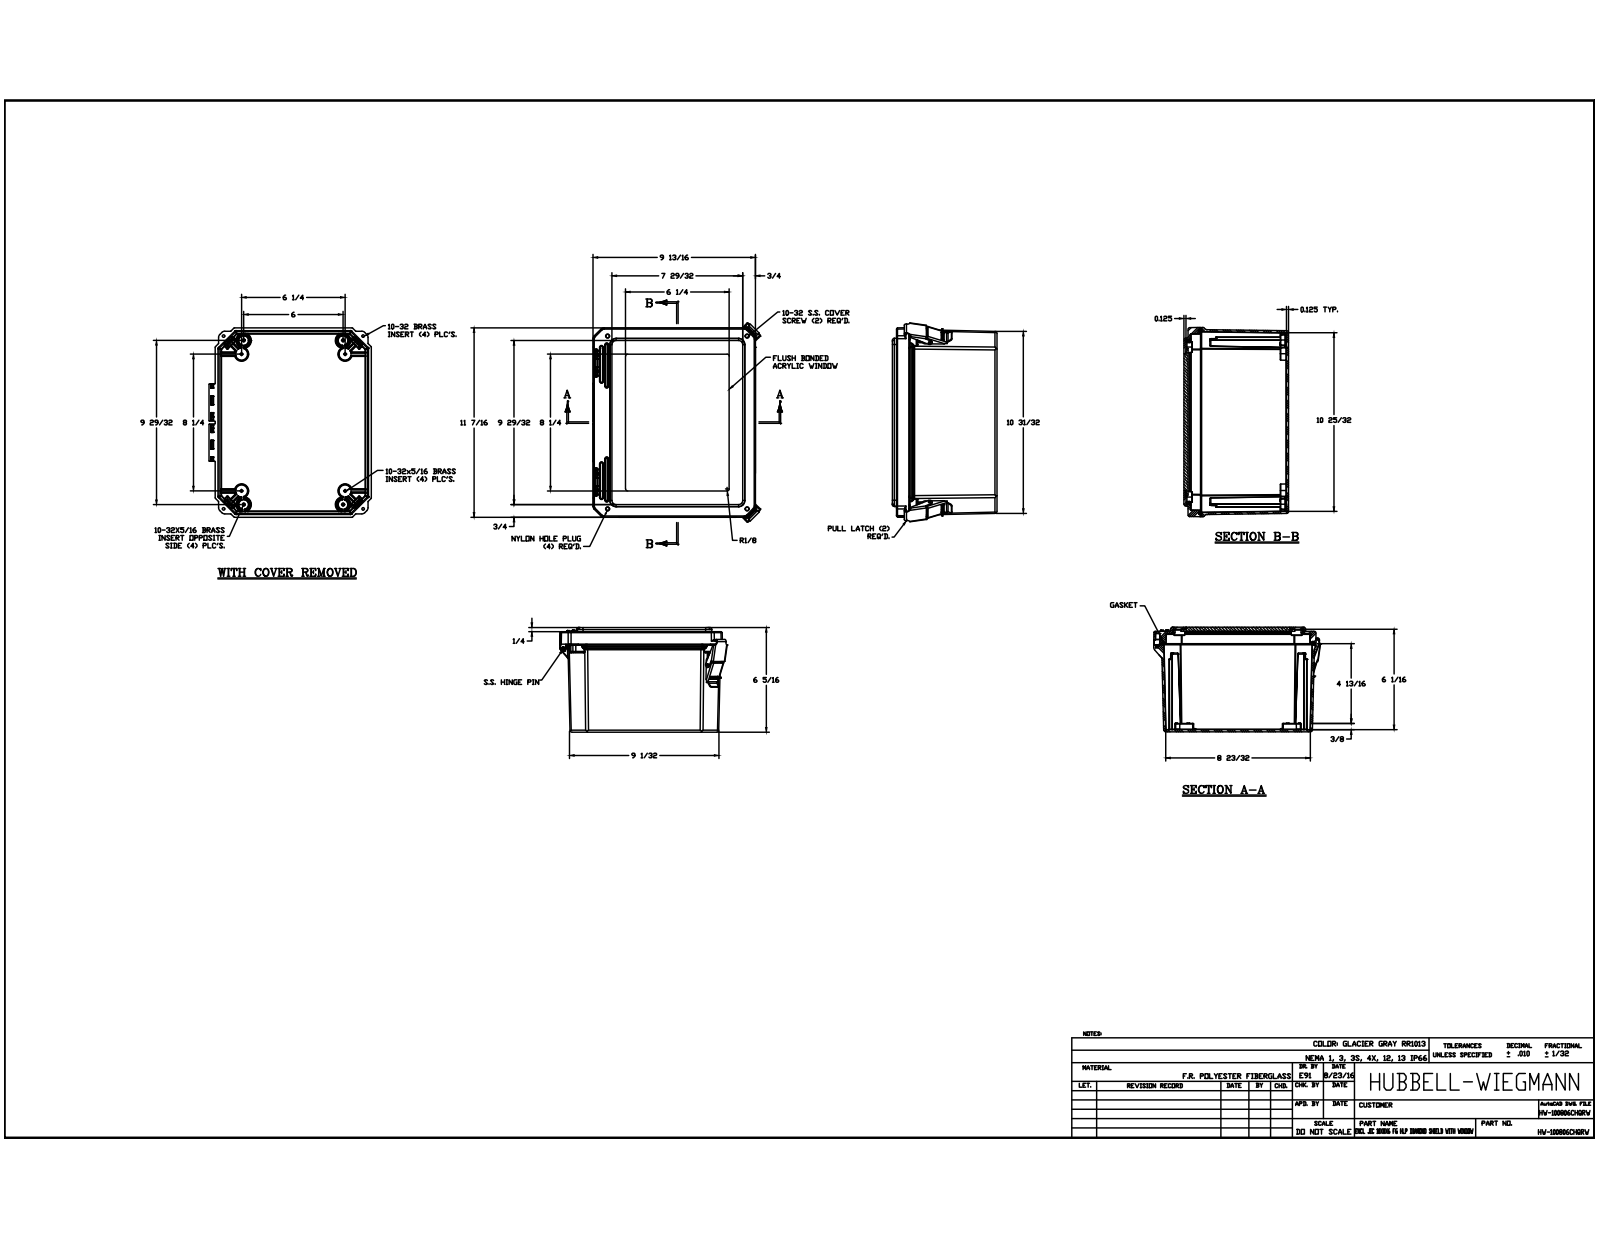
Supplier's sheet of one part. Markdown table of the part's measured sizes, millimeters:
| quantity | value |
| --- | --- |
| part name | DSW100806HPL_STP; DS100806BOX; BRASS INSERT-(; BRASS INSERT-(_1 (+8 more) |
| STEP written by | Autodesk Inventor 2017 (AUTOMOTIVE_DESIGN) |
| units | millimeters |
| bodies | 34 solids, 2226 faces (770 planar, 892 cylindrical, 564 other) |
| overall size | 307.69 × 257.75 × 160.28 |
| volume | 1 260 000 mm³ |
| surface area | 669 173 mm² |
| round holes (diameter × count) | 3.96 × 16, 3.43 × 11, 3.86 × 8, 3.81 × 4, 6.4 × 4, 6.43 × 4, 3.43 × 2, 5.56 × 2, 5.77 × 2, 7.94 × 2, 9.52 × 2, 3.48 × 1 |
| round bosses / shafts (diameter × count) | 6.25 × 16, 22.1 × 4, 7.62 × 4, 5.3 × 4, 11.05 × 2, 3.43 × 1 |
| partial cylindrical surfaces (radius × count) | 0.25 × 157, 0.13 × 80, 0.76 × 63, 0.51 × 57, 1.52 × 34, 1.59 × 26, 2.29 × 26, 3.17 × 26 |
| main face-to-face distances | 3.18, 3.23, 3.2, 160.28, 157.1, 154.57, 151.39, 5.71, 153.93, 3.17 |
| hole center spacings | 6.35, 188.36, 31.49, 39.01, 156.96, 183.28, 238.73, 278.01 |
